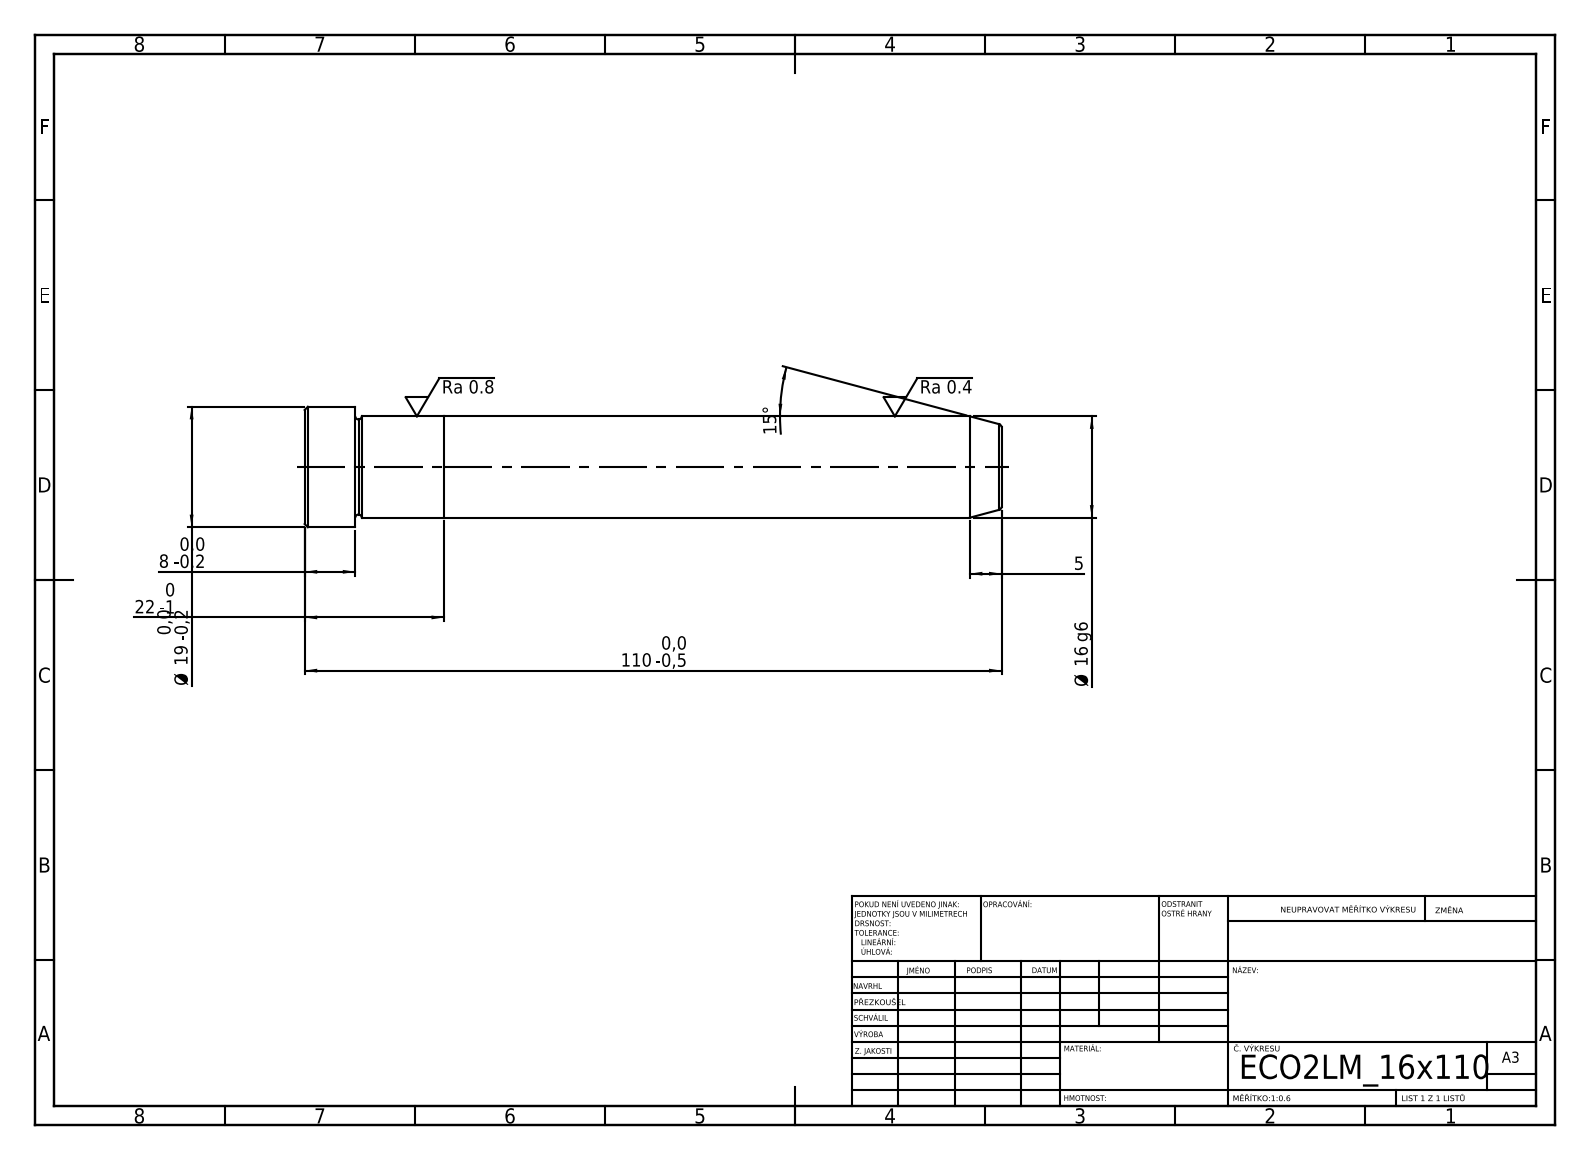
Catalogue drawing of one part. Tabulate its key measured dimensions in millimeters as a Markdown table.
| quantity | value |
| --- | --- |
| STEP written by | SolidWorks 2019 (CONFIG_CONTROL_DESIGN) |
| units | millimeters |
| bodies | 2 solids, 21 faces (5 planar, 6 cylindrical, 10 other) |
| overall size | 110 × 19 × 19 |
| volume | 22 590 mm³ |
| surface area | 6 502 mm² |
| round bosses / shafts (diameter × count) | 19 × 1, 16 × 1 |
| main face-to-face distances | 22, 88, 110, 102, 14, 8 |
